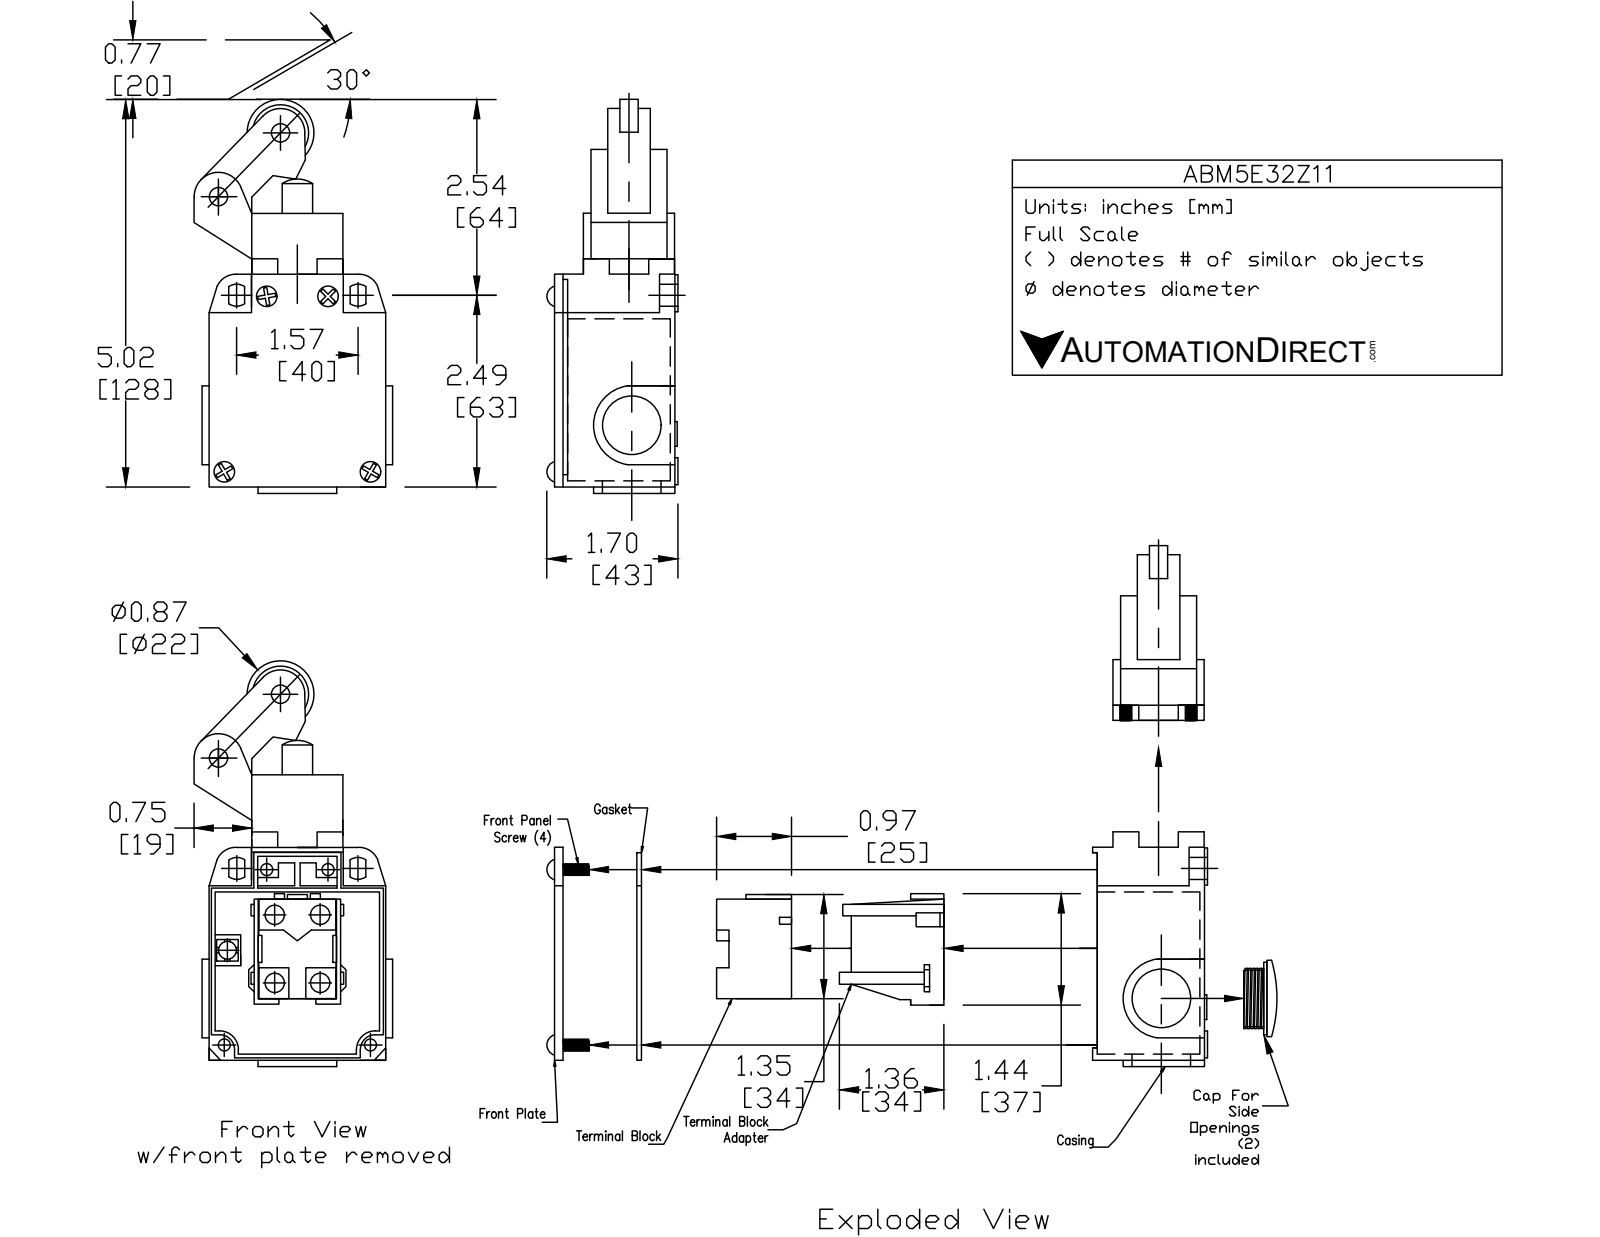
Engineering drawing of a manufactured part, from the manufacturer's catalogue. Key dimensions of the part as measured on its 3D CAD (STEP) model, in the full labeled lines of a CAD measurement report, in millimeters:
Part name (STEP PRODUCT): ABM5E32Z11
STEP written by: SolidWorks 2017 (AUTOMOTIVE_DESIGN)
Units: millimetres
Bodies: 4 solids, 221 faces (108 planar, 90 cylindrical, 23 other)
Overall size (bounding box): 134.3 × 54 × 43.3
Volume: 140 600 mm³ · Surface area: 32 730 mm²
Round holes (diameter × count): ⌀5.2 ×2, ⌀10 ×1, ⌀17 ×1, ⌀19 ×1
Round bosses / shafts (diameter × count): ⌀10 ×5, ⌀7 ×3, ⌀22 ×1, ⌀11.5 ×1
Partial cylindrical surfaces — rounded edges, fillets, slot ends (radius × count): R1.5 ×16, R1 ×5, R5 ×4, R3.3 ×2, R8 ×2, R12 ×2, R6 ×1, R11.5 ×1
Main face-to-face distances: 40, 8.3, 39.5, 3, 5, 18.7, 30, 21.7, 11.3, 10.5
Hole centre spacings: 1, 67.1
